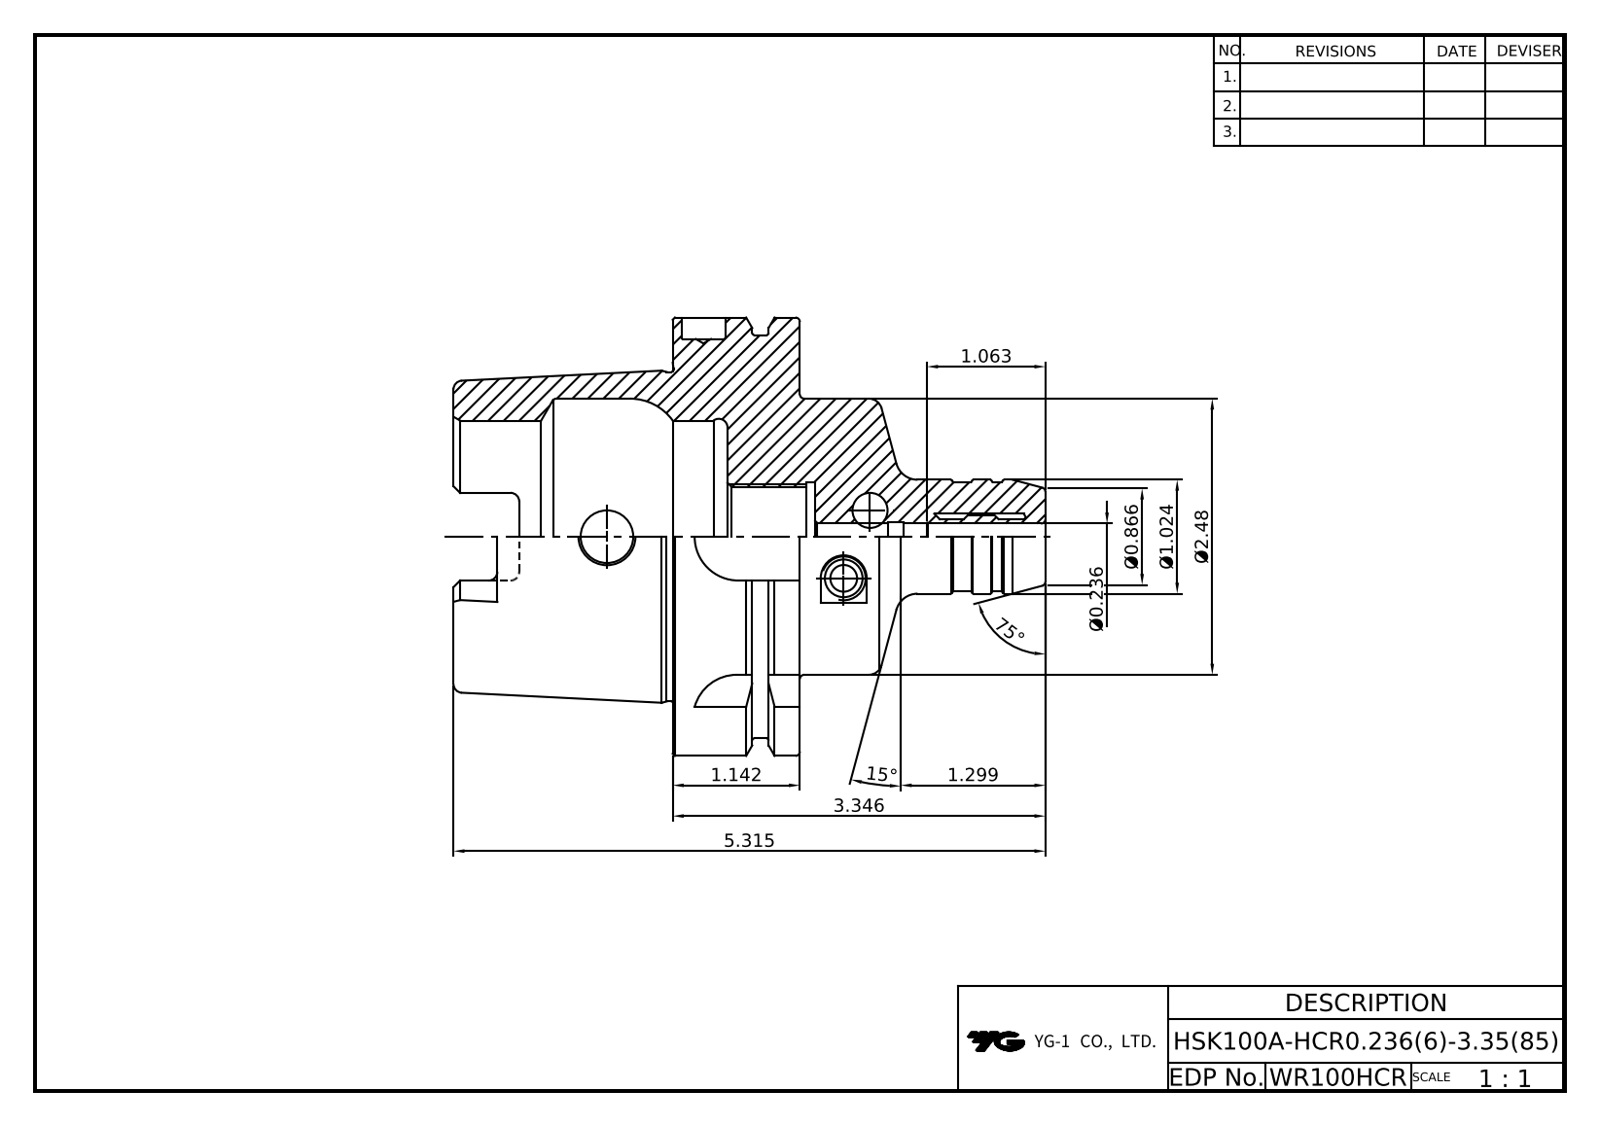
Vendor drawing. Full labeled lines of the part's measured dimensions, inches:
Part name (STEP PRODUCT): LO-HSK100A-HCR6-85
STEP written by: Autodesk Inventor 2025 (AUTOMOTIVE_DESIGN)
Units: inches
Bodies: 1 solid, 134 faces (38 planar, 39 cylindrical, 57 other)
Overall size (bounding box): 5.315 × 3.937 × 3.937
Volume: 20.36 in³ · Surface area: 87.78 in²
Round holes (diameter × count): ⌀0.236 ×1, ⌀0.244 ×1, ⌀0.26 ×1, ⌀0.394 ×1, ⌀0.472 ×1, ⌀0.881 ×1, ⌀2.087 ×1, ⌀2.48 ×1
Round bosses / shafts (diameter × count): ⌀3.937 ×1, ⌀3.622 ×1, ⌀2.969 ×1, ⌀1.024 ×1, ⌀0.984 ×1
Partial cylindrical surfaces — rounded edges, fillets, slot ends (radius × count): R0.079 ×6, R0.192 ×4, R0.394 ×4
Main face-to-face distances: 1.142, 0.492, 0.65, 2.461, 1.969, 3.11, 3.091, 1.122, 0.63, 0.02
